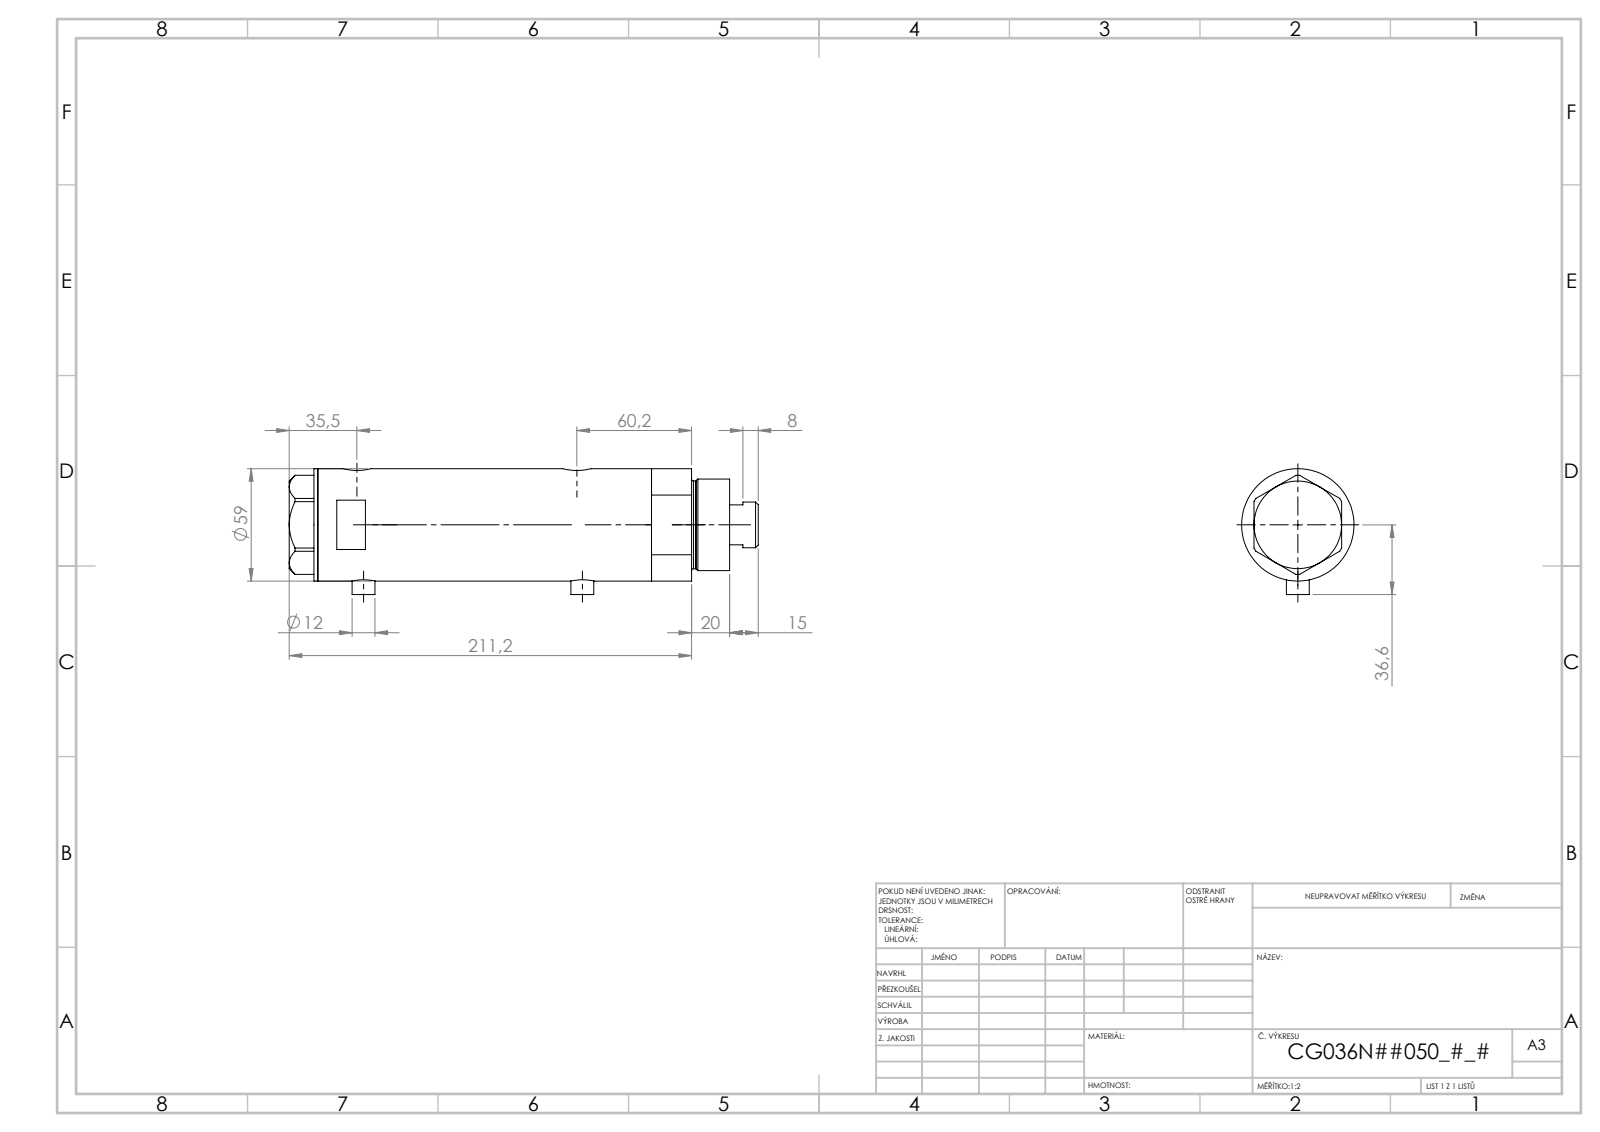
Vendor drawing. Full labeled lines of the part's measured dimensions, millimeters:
Part name (STEP PRODUCT): V270CG_VC; V270CG_FRONT; V270CG_BACK; V270CG_MIDDLE
STEP written by: SolidWorks 2019 (CONFIG_CONTROL_DESIGN)
Units: millimetres
Bodies: 4 solids, 126 faces (53 planar, 53 cylindrical, 20 other)
Overall size (bounding box): 213.42 × 60.1 × 59
Volume: 481 490 mm³ · Surface area: 100 743 mm²
Round holes (diameter × count): ⌀5 ×2, ⌀9.73 ×2, ⌀12.5 ×2, ⌀15 ×2, ⌀8.5 ×1, ⌀25 ×1, ⌀26.5 ×1, ⌀36 ×1, ⌀40 ×1, ⌀52 ×1
Round bosses / shafts (diameter × count): ⌀12 ×2, ⌀59 ×1, ⌀48 ×1, ⌀46 ×1, ⌀24 ×1
Main face-to-face distances: 107.35, 38.5, 122.35, 83.85, 15, 15.01, 23.5, 23.49, 107.34, 183.43
Hole centre spacings: 2.9, 3.5, 82.15, 85.05, 85.65, 88.55, 2.89, 2.91
